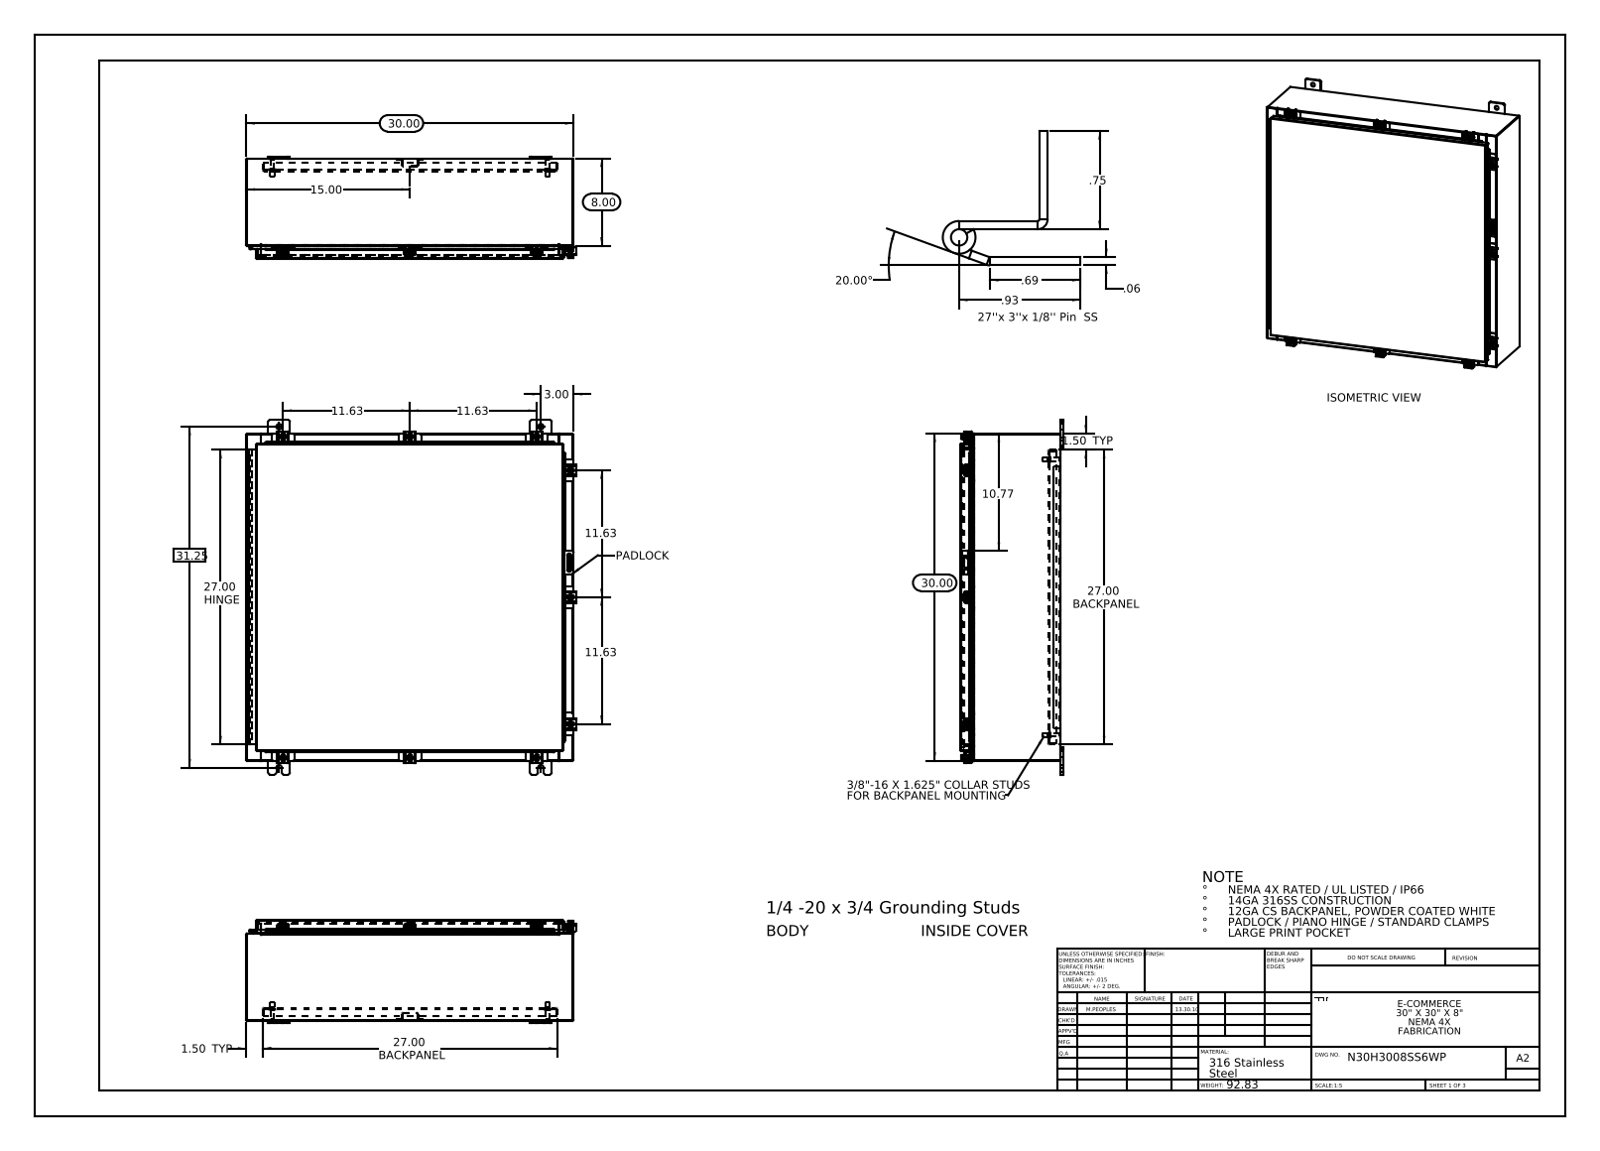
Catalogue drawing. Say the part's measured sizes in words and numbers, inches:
The part is named "N30H3008SS6WP Top; N30H3008SS6WP Mounting Studs; N30H3008SS6WP Backpanel; N30H3008SS6WP (+8 more)". Its 3-D file was written by "SolidWorks 2013 (CONFIG_CONTROL_DESIGN)". It is 63 solids with 2262 faces: 1206 planar, 936 cylindrical and 120 other. Overall it measures 32.5 by 30.211 by 9.389 inches. Its volume is 325.9 cubic inches and its surface area 8 130 square inches. Round holes: 9 of diameter 0.213, 9 of diameter 0.26, 8 of diameter 0.5, 2 of diameter 0.125, 1 of diameter 0.125. Round bosses or shafts: 10 of diameter 0.25, 9 of diameter 0.5, 9 of diameter 0.399, 4 of diameter 0.625, 4 of diameter 0.375, 4 of diameter 0.33. Partial cylindrical surfaces (rounded edges, fillets, slot ends): 42 of radius 0.06, 31 of radius 0.013, 25 of radius 0.088, 24 of radius 0.19, 18 of radius 0.12, 18 of radius 0.141, 13 of radius 0.05, 12 of radius 0.08. The main face-to-face distances are 0.075, 9.126, 29.925, 9.051, 9.201, 0.104, 1, 8.126, 1.075, 8.051. The hole center spacings are 2.326, 11.625, 12.798, 15.048, 27.369, 30.124, 31.663, 36.553.
